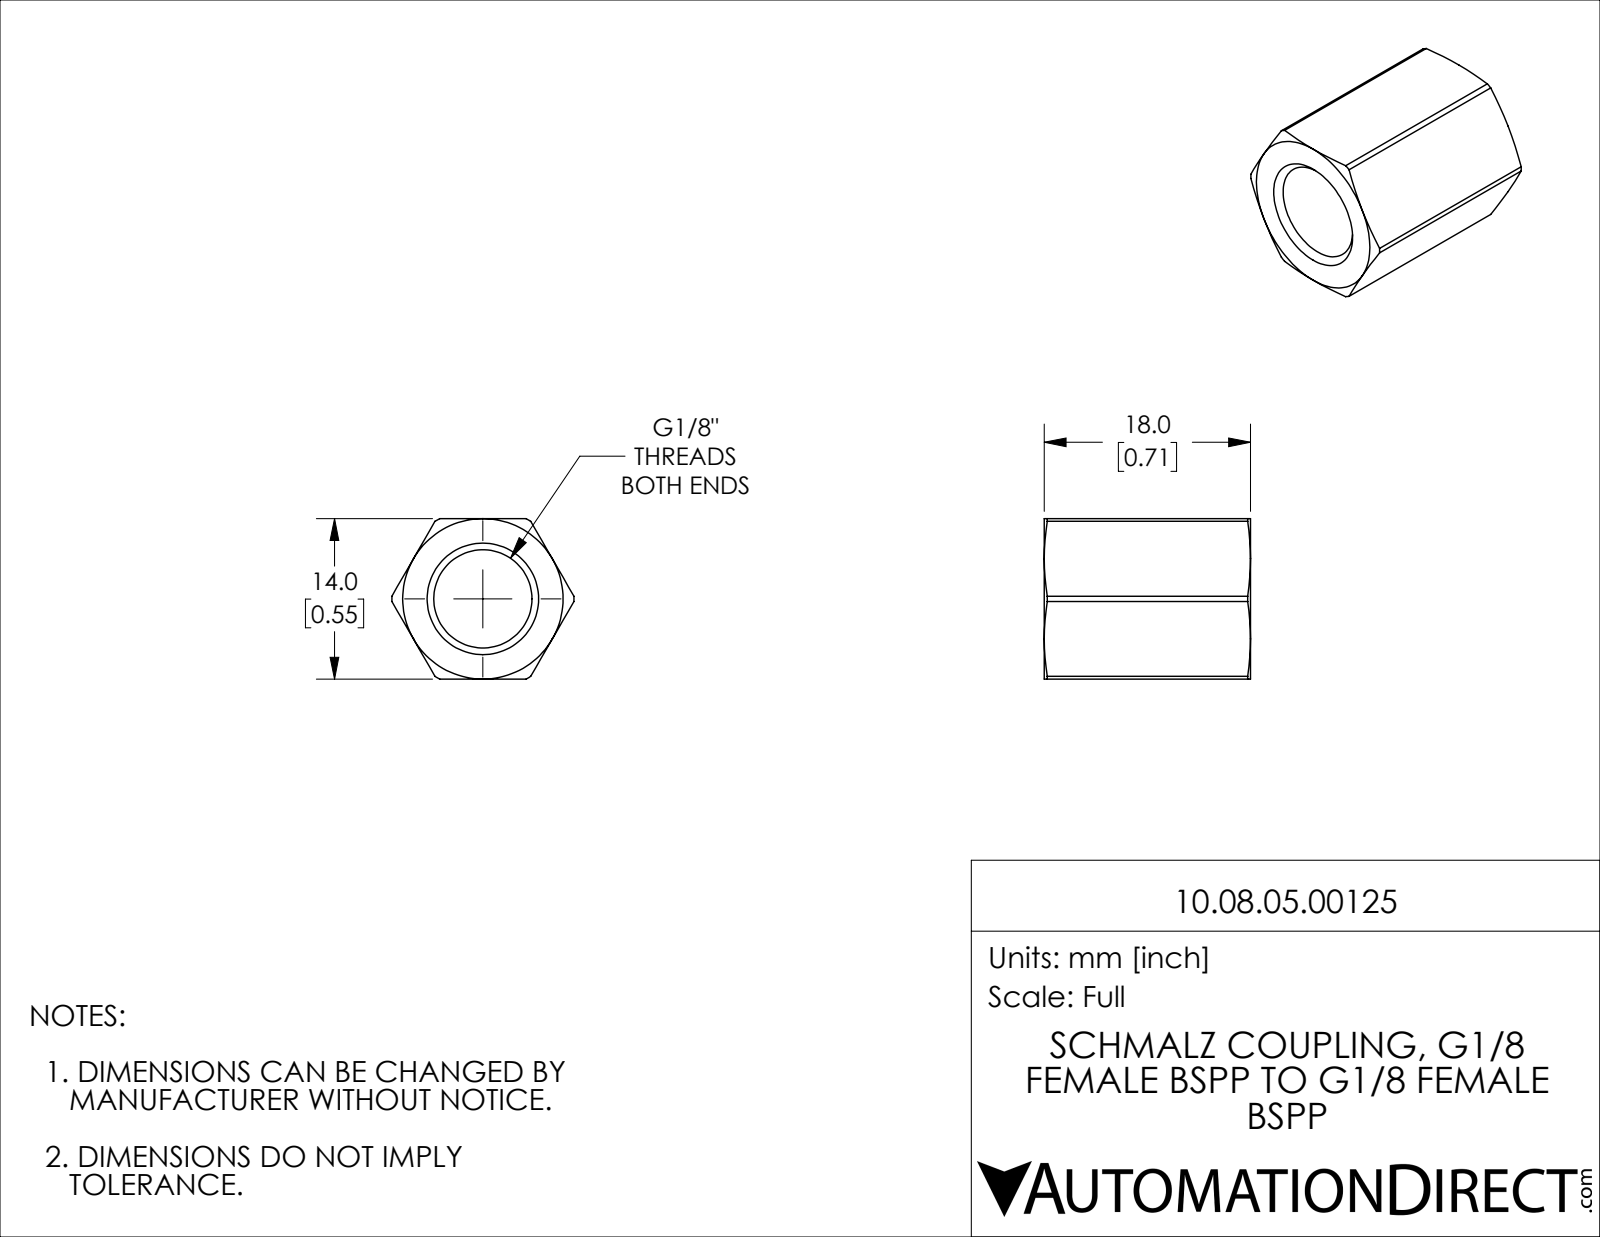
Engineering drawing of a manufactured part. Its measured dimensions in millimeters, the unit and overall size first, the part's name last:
Units: millimetres
Overall size (bounding box): 18 × 15.9 × 14
Round holes (diameter × count): ⌀8.57 ×1
Partial cylindrical surfaces — rounded edges, fillets, slot ends (radius × count): R7.95 ×1
Main face-to-face distances: 14, 18
Volume: 2 001 mm³ · Surface area: 1 548 mm²
Bodies: 1 solid, 32 faces (8 planar, 8 cylindrical, 16 other)
Part name (STEP PRODUCT): 10.08.05.00125
STEP written by: SolidWorks 2021 (CONFIG_CONTROL_DESIGN)
